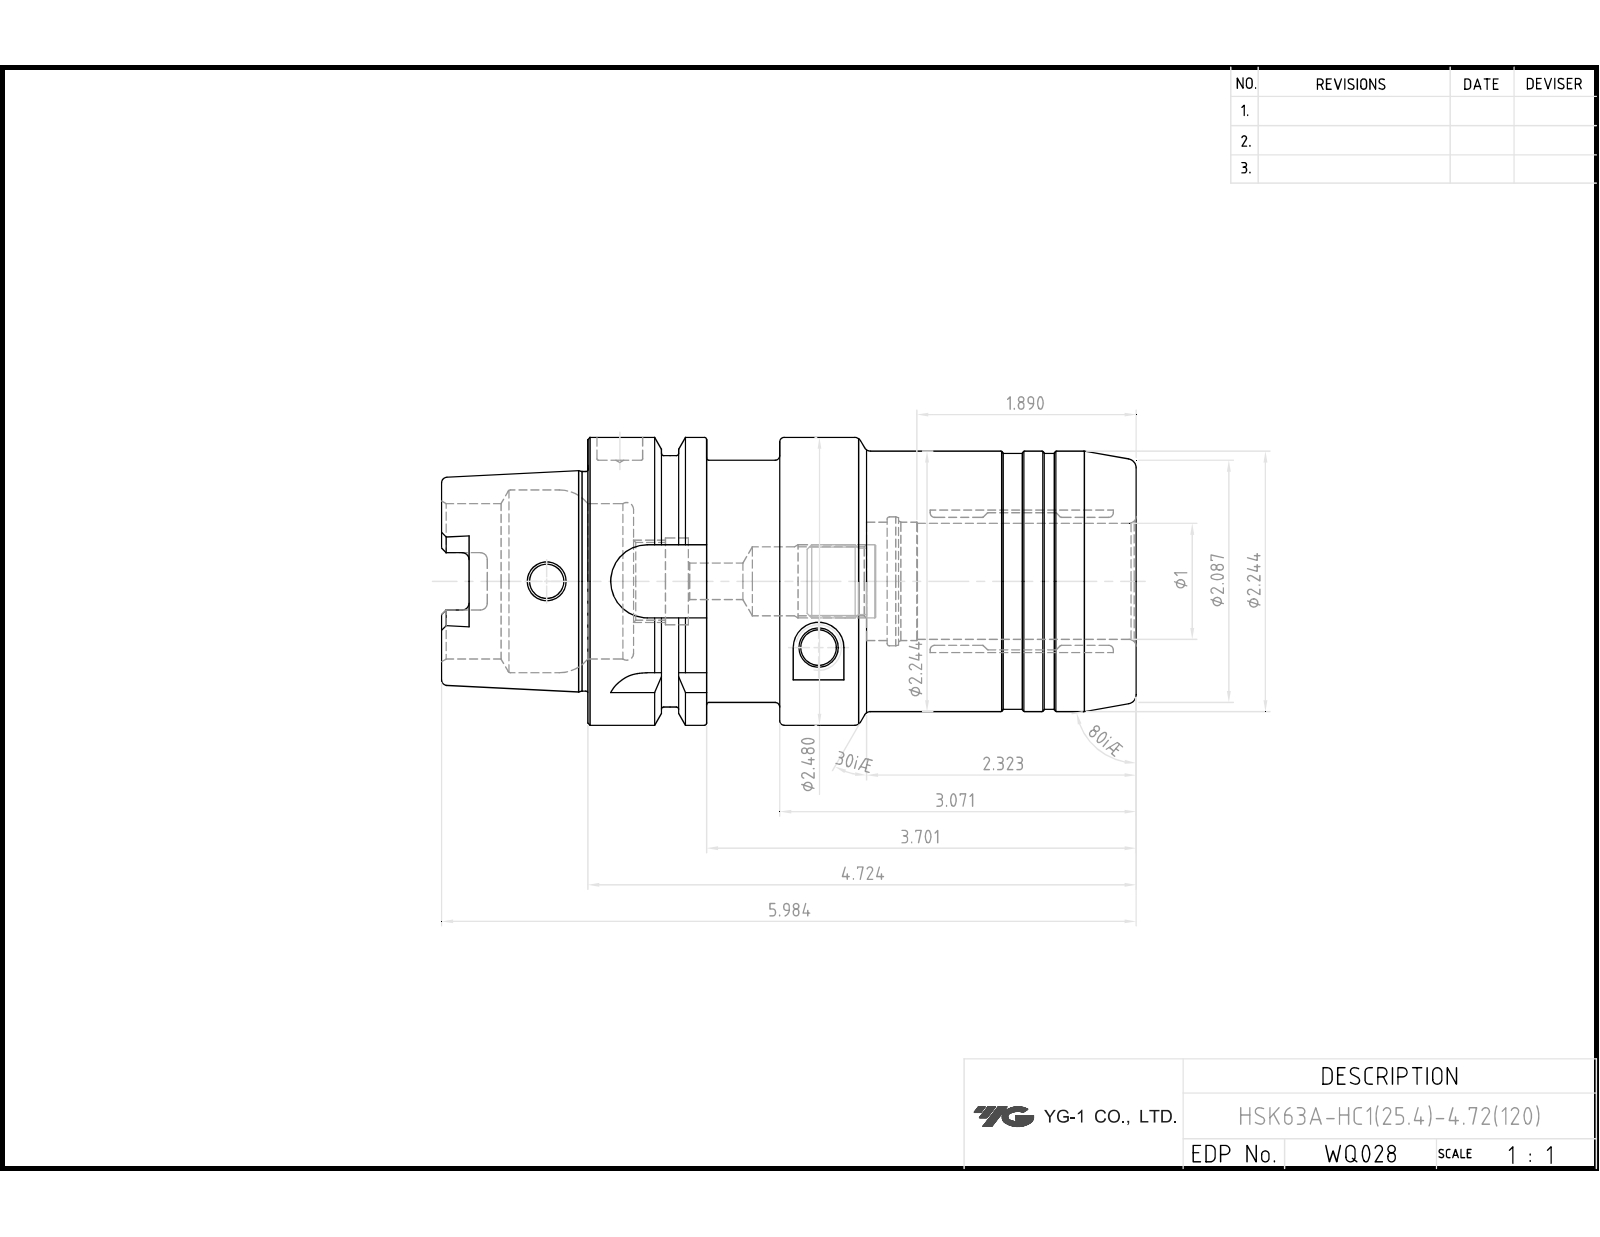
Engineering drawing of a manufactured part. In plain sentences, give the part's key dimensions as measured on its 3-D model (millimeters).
The part is named "WQ028-HSK63A-HC1-4_72". Its 3-D file was written by "CREO PARAMETRIC BY PTC INC, 2018100 (CONFIG_CONTROL_DESIGN)". It is 1 solid with 239 faces: 69 planar, 68 cylindrical and 102 other. Overall it measures 152 by 63 by 63 millimeters. Its volume is 287 374 cubic millimeters and its surface area 47 895 square millimeters. Round holes: 2 of diameter 10, 1 of diameter 7.5, 1 of diameter 8.4, 1 of diameter 15, 1 of diameter 16, 1 of diameter 17, 1 of diameter 18, 1 of diameter 19, 1 of diameter 25.4, 1 of diameter 25.8, 1 of diameter 34, 1 of diameter 40. Round bosses or shafts: 1 of diameter 63, 1 of diameter 57, 1 of diameter 56, 1 of diameter 55, 1 of diameter 53, 1 of diameter 48.04. Partial cylindrical surfaces (rounded edges, fillets, slot ends): 6 of radius 1.5, 4 of radius 2.88, 4 of radius 8, 1 of radius 5.55. The main face-to-face distances are 16, 32, 120, 42, 26, 10, 94, 78, 110, 74. The hole center spacings are 61.24.
